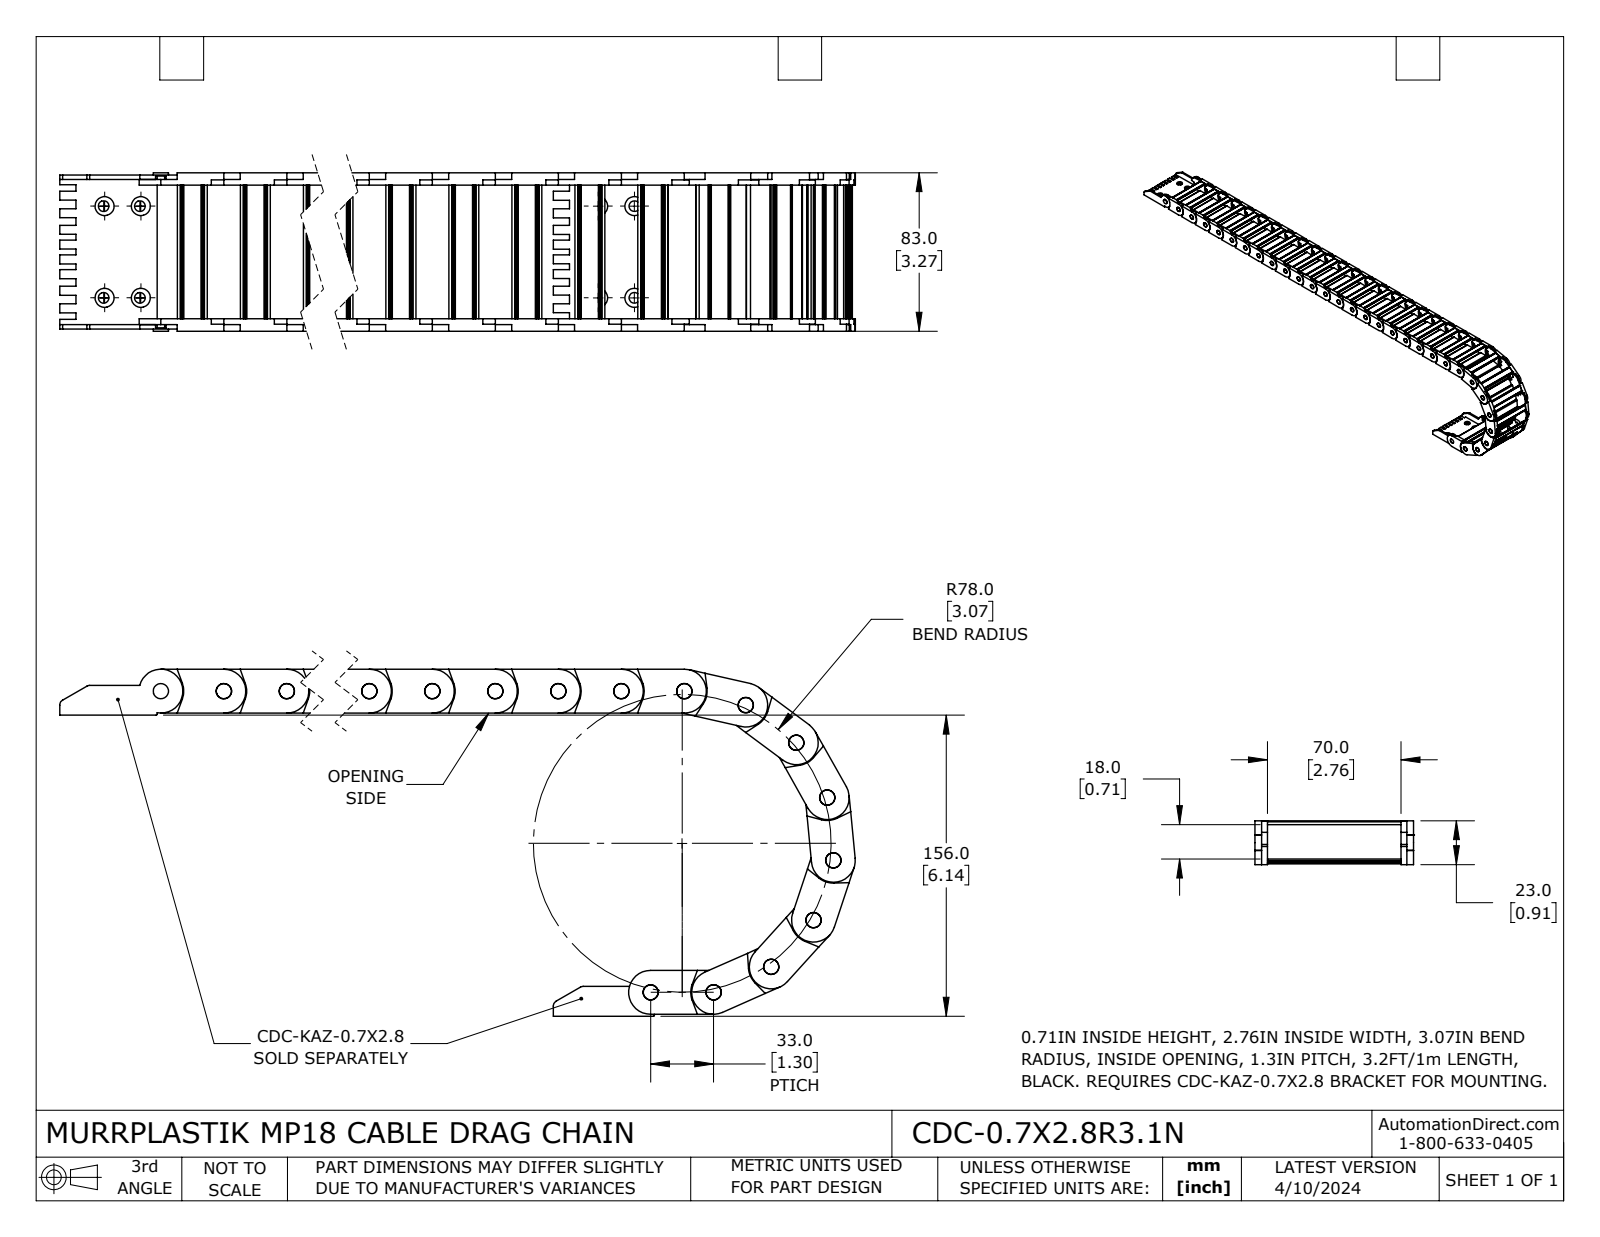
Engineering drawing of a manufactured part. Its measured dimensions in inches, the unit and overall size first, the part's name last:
Units: inches
Overall size (bounding box): 32.555 × 7.115 × 3.268
Round holes (diameter × count): ⌀0.315 ×30
Round bosses / shafts (diameter × count): ⌀0.315 ×1
Partial cylindrical surfaces — rounded edges, fillets, slot ends (radius × count): R0.02 ×120, R0.059 ×120, R0.008 ×60, R0.012 ×60, R0.453 ×31, R0.47 ×31, R0.197 ×30, R0.215 ×30
Main face-to-face distances: 0.256, 3.012, 0.079, 3.268, 0.138, 3.13, 0.118, 2.874, 0.146, 3.122
Hole centre spacings: 1.299, 2.598, 3.898, 5.197, 6.496, 7.795, 9.094, 10.394
Volume: 23.09 in³ · Surface area: 469.9 in²
Bodies: 30 solids, 2370 faces (1110 planar, 1260 cylindrical, 0 other)
Part name (STEP PRODUCT): CDC-0.7X2.8R3.1N
STEP written by: SolidWorks 2023 (CONFIG_CONTROL_DESIGN)
